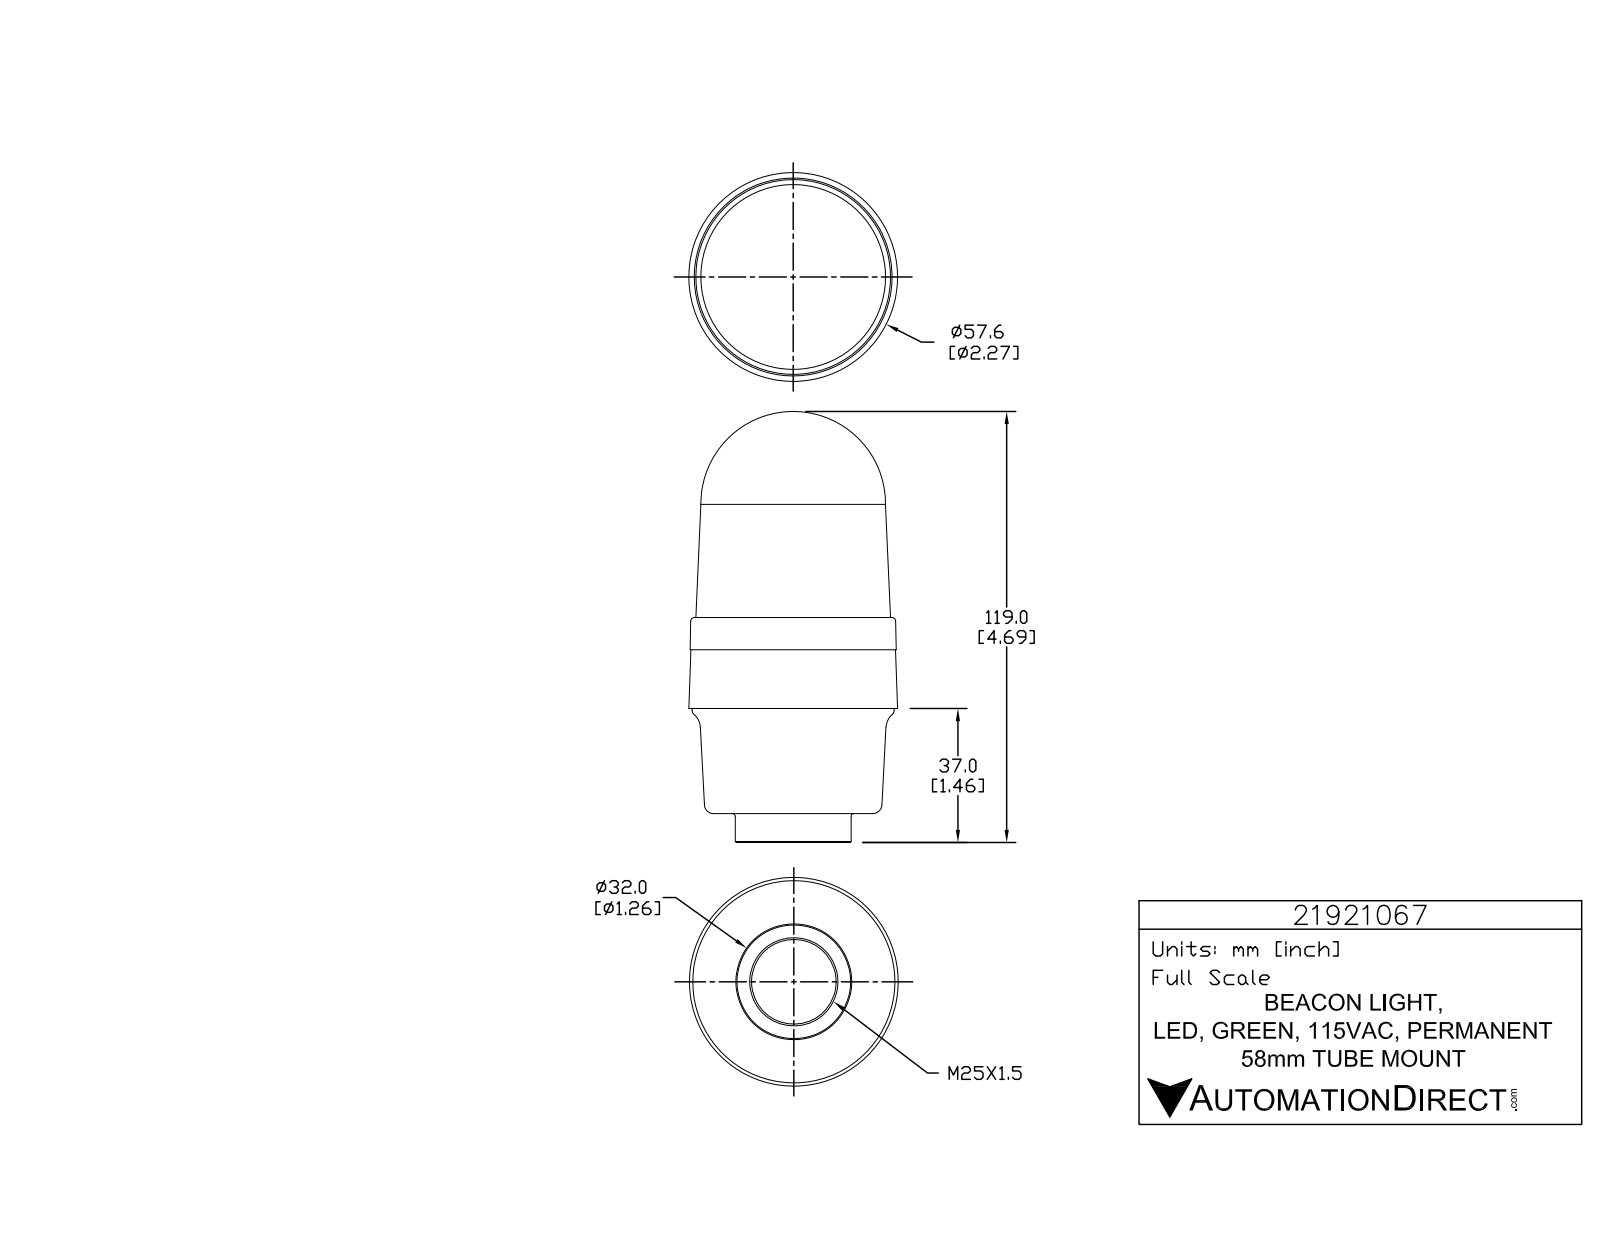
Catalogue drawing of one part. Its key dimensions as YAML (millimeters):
part_name: "21921067"
step_written_by: "SolidWorks 2015 (AUTOMOTIVE_DESIGN)"
units: millimeters
bodies: {solids: 1, faces: 791, planar: 525, cylindrical: 168, other: 98}
overall_size: [119, 57.6, 57.6]
volume: 227600
surface_area: 21970
round_holes:
  - {diameter: 1, count: 3}
  - {diameter: 23.4, count: 1}
round_bosses_or_shafts:
  - {diameter: 5.7, count: 3}
  - {diameter: 1.4, count: 3}
  - {diameter: 55.8, count: 1}
  - {diameter: 32, count: 1}
partial_cylinders:
  - {radius: 0.2, count: 6}
  - {radius: 0.2, count: 6}
  - {radius: 0.2, count: 6}
  - {radius: 3.3, count: 6}
  - {radius: 0.1, count: 3}
  - {radius: 0.1, count: 3}
  - {radius: 0.2, count: 3}
  - {radius: 0.2, count: 3}
face_to_face_distances: [8, 29, 37, 25.1, 54.1, 62.1, 8.9, 16.2, 45.2, 53.2]
